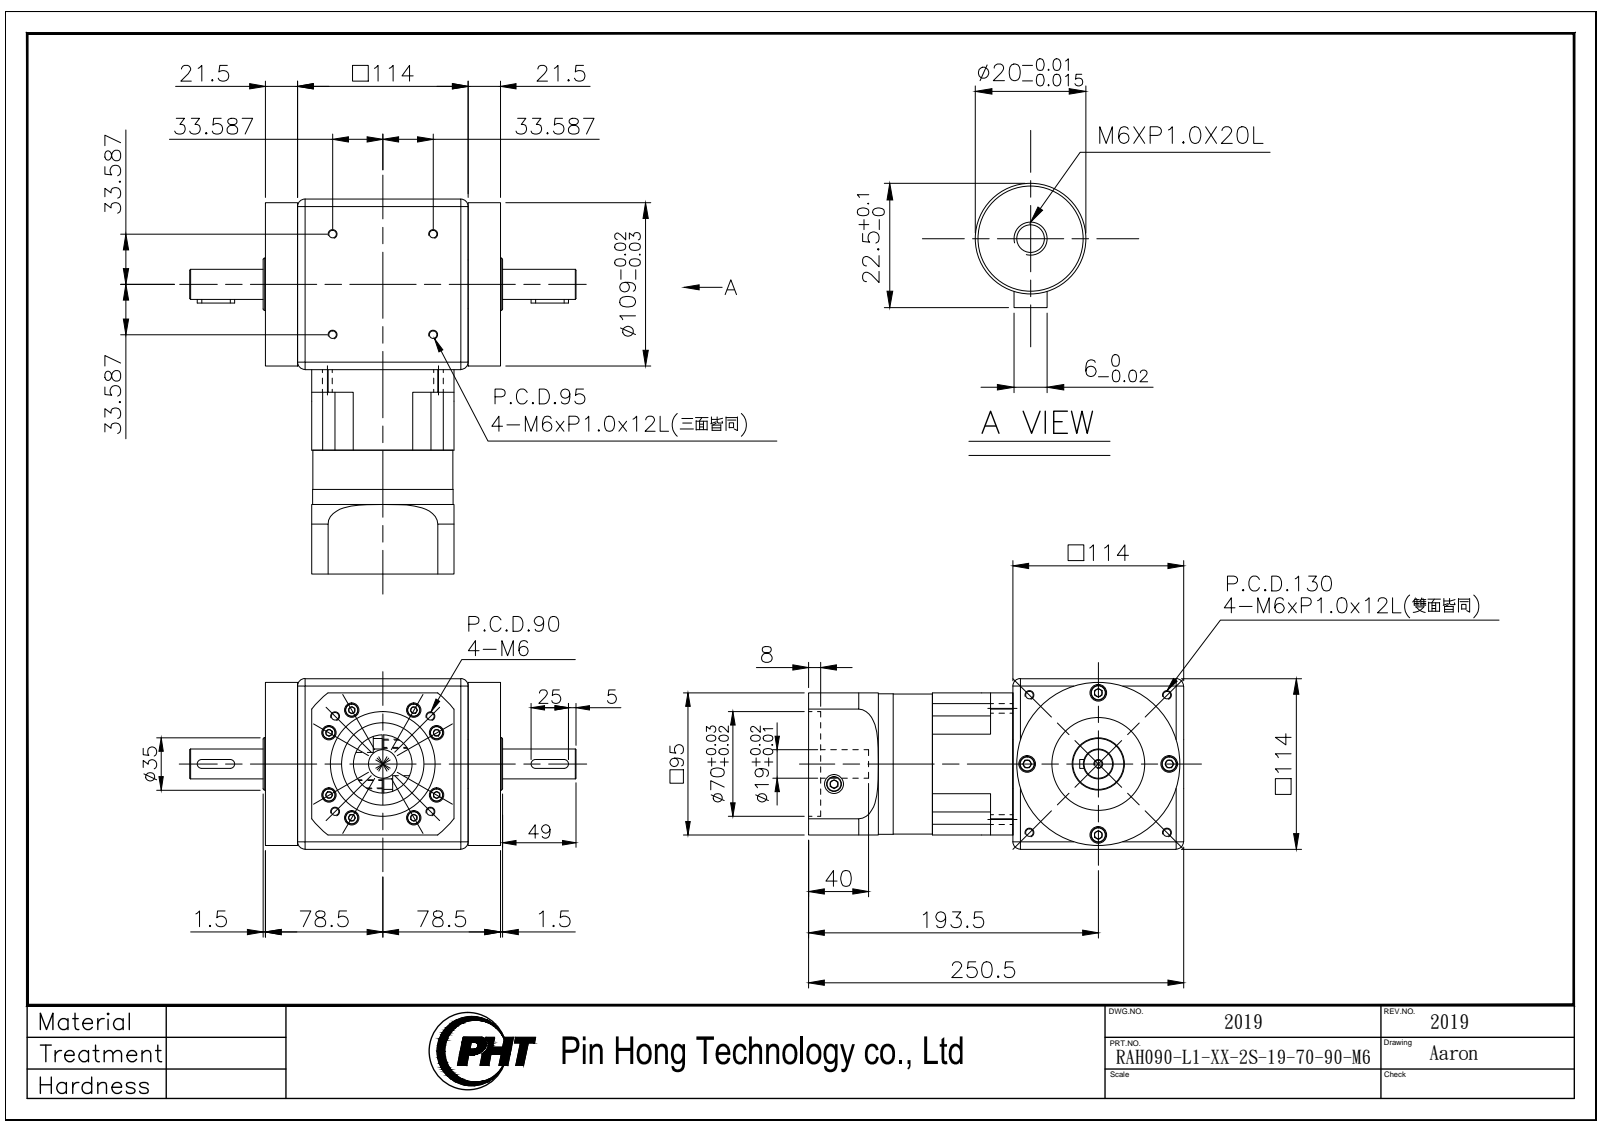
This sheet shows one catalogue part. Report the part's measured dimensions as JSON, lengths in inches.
{"part_name": "RAH090-L1-XX-2S-19-70-90-M6_2019", "step_written_by": "SolidWorks 2016 (AUTOMOTIVE_DESIGN)", "units": "inches", "bodies": {"solids": 2, "faces": 684, "planar": 314, "cylindrical": 236, "other": 134}, "overall_size": [10.157, 9.862, 4.488], "volume_in3": 176.7, "surface_area_in2": 323.3, "round_holes": [[0.197, 17], [0.205, 8], [0.374, 8], [0.26, 4], [0.268, 4], [0.433, 4], [0.5, 2], [0.098, 1], [0.748, 1], [2.165, 1], [2.756, 1]], "round_bosses_or_shafts": [[0.394, 8], [0.335, 8], [4.291, 1], [3.693, 1], [3.681, 1], [3.15, 1], [2.441, 1], [1.535, 1]], "partial_cylinders_radius": [[0.118, 4], [0.236, 4], [2.047, 1], [2.362, 1], [3.114, 1]], "face_to_face_distances": [4.488, 4.114, 0.374, 1.22, 3.74, 4.961, 0.846, 6.181, 5.335, 0.118], "hole_center_spacings": [1.634, 2.645, 0.465, 0.514, 0.646, 1.811, 1.87, 2.076]}
